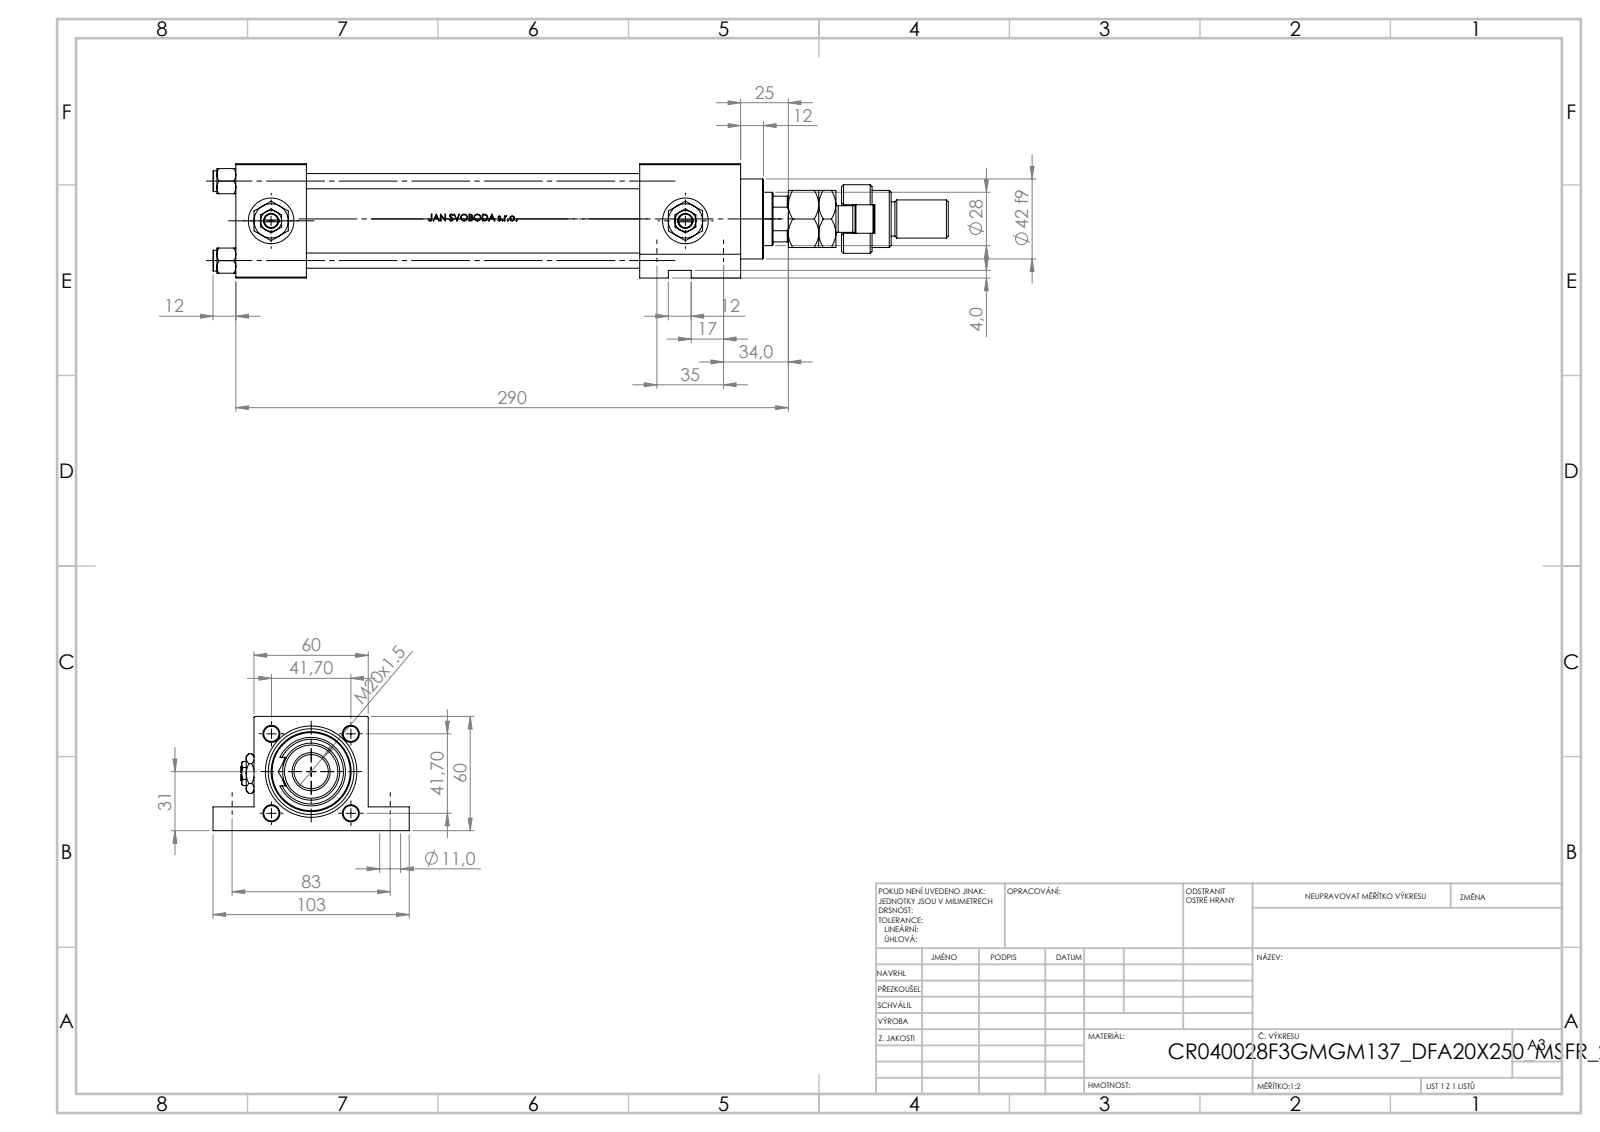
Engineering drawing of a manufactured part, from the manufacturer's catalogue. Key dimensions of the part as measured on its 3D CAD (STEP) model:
Part name (STEP PRODUCT): V215CR_F_Body; MFA; V215_VC_A; V215CR_VCP_F (+4 more)
STEP written by: SolidWorks 2019 (CONFIG_CONTROL_DESIGN)
Units: millimetres
Bodies: 15 solids, 1300 faces (512 planar, 162 cylindrical, 626 other)
Overall size (bounding box): 386 × 103 × 60
Volume: 633 664 mm³ · Surface area: 187 532 mm²
Round holes (diameter × count): ⌀8 ×4, ⌀11 ×4, ⌀16.66 ×3, ⌀24 ×3, ⌀7 ×2, ⌀16 ×1, ⌀18.5 ×1, ⌀28 ×1, ⌀31 ×1, ⌀40 ×1, ⌀45 ×1
Round bosses / shafts (diameter × count): ⌀11 ×4, ⌀46 ×1, ⌀42 ×1, ⌀36 ×1, ⌀30 ×1, ⌀22 ×1, ⌀20 ×1, ⌀18 ×1
Partial cylindrical surfaces — rounded edges, fillets, slot ends (radius × count): R7.5 ×1, R12 ×1, R13.5 ×1
Main face-to-face distances: 60, 37, 53, 212, 175, 265, 38, 228, 12.5, 47.5
Hole centre spacings: 41.7, 28.79, 30.2, 35, 58.97, 83, 90.08, 8
